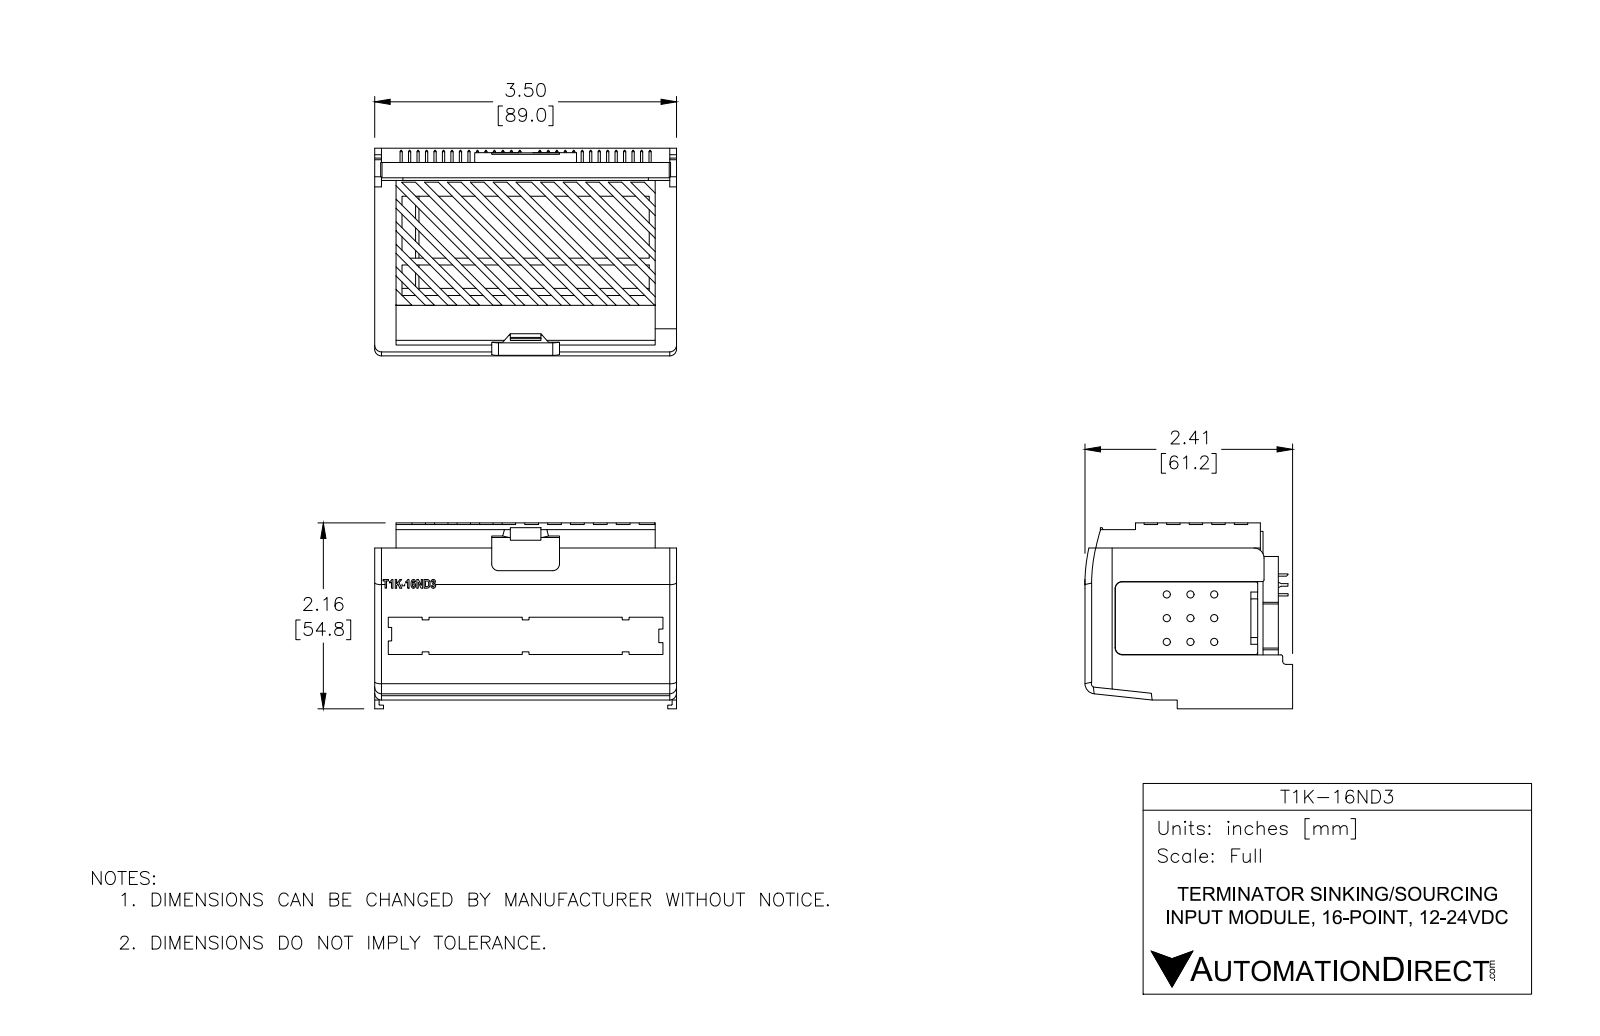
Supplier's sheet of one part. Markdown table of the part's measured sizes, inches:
| quantity | value |
| --- | --- |
| part name | T1K-16ND3 |
| STEP written by | SolidWorks 2013 (AUTOMOTIVE_DESIGN) |
| units | inches |
| bodies | 1 solid, 649 faces (440 planar, 181 cylindrical, 28 other) |
| overall size | 3.492 × 2.563 × 2.416 |
| volume | 2.774 in³ |
| surface area | 84.51 in² |
| round holes (diameter × count) | 0.118 × 16 |
| round bosses / shafts (diameter × count) | 0.028 × 56 |
| partial cylindrical surfaces (radius × count) | 0.138 × 18, 0.039 × 5, 0.01 × 3, 0.022 × 3, 0.059 × 2, 0.315 × 1, 0.394 × 1, 0.709 × 1 |
| main face-to-face distances | 0.079, 3.413, 2.179, 0.02, 2.354, 3.492, 0.059, 2.176, 2.1, 3.335 |
| hole center spacings | 0.203, 0.406, 0.608, 0.811, 1.014, 1.217, 1.419, 1.622 |
